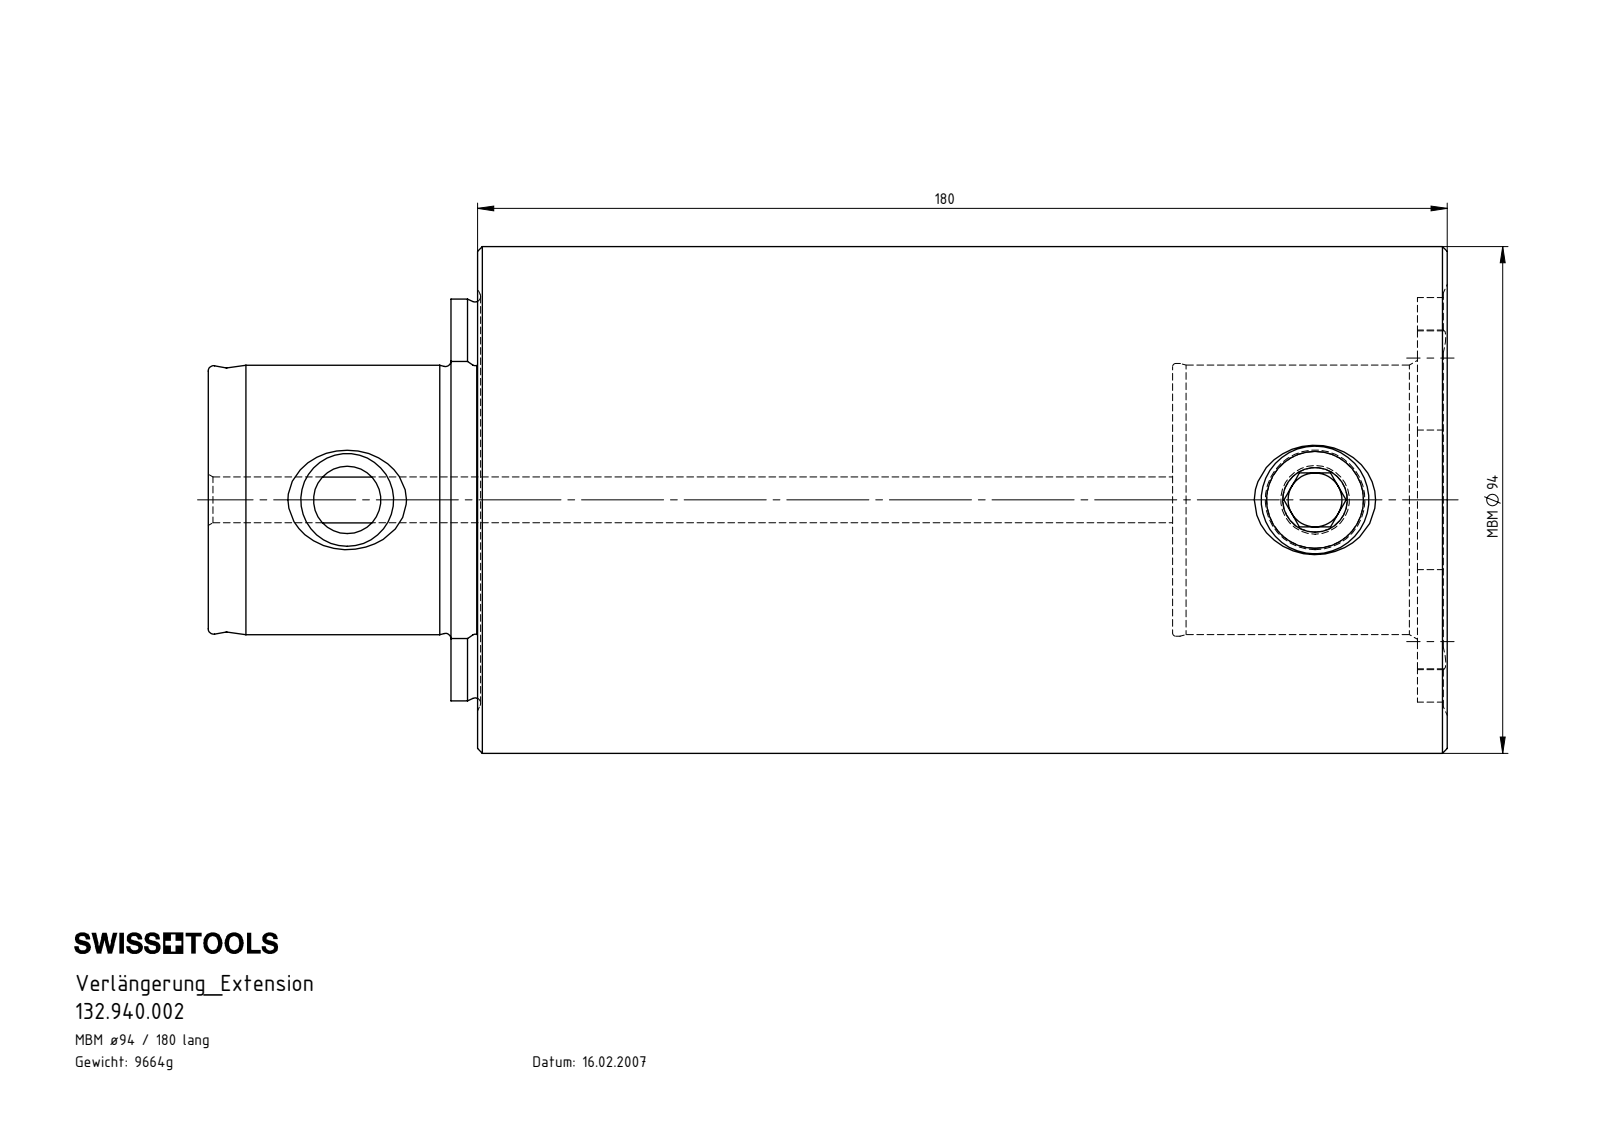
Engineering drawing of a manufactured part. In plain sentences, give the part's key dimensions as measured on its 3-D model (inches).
The part is named "MB9.MB9.K01.180; MB9-MB9.K01.180_B; MB9-ER1.001.032_A". Its 3-D file was written by "SolidWorks 2011 (CONFIG_CONTROL_DESIGN)". It is 2 solids with 121 faces: 28 planar, 32 cylindrical and 61 other. Overall it measures 9.055 by 3.701 by 3.701 inches. Its volume is 75.12 cubic inches and its surface area 142.5 square inches. Round holes: 1 of diameter 0.335, 1 of diameter 0.492, 1 of diameter 0.728, 1 of diameter 1.969, 1 of diameter 1.992. Round bosses or shafts: 1 of diameter 3.701, 1 of diameter 0.787. Partial cylindrical surfaces (rounded edges, fillets, slot ends): 4 of radius 0.205, 1 of radius 1.181, 1 of radius 1.467, 1 of radius 1.477. The main face-to-face distances are 7.063, 5.079, 7.087, 2.008, 1.969, 7.047, 9.055, 8.837, 6.868, 1.789. The hole center spacings are 7.073.
